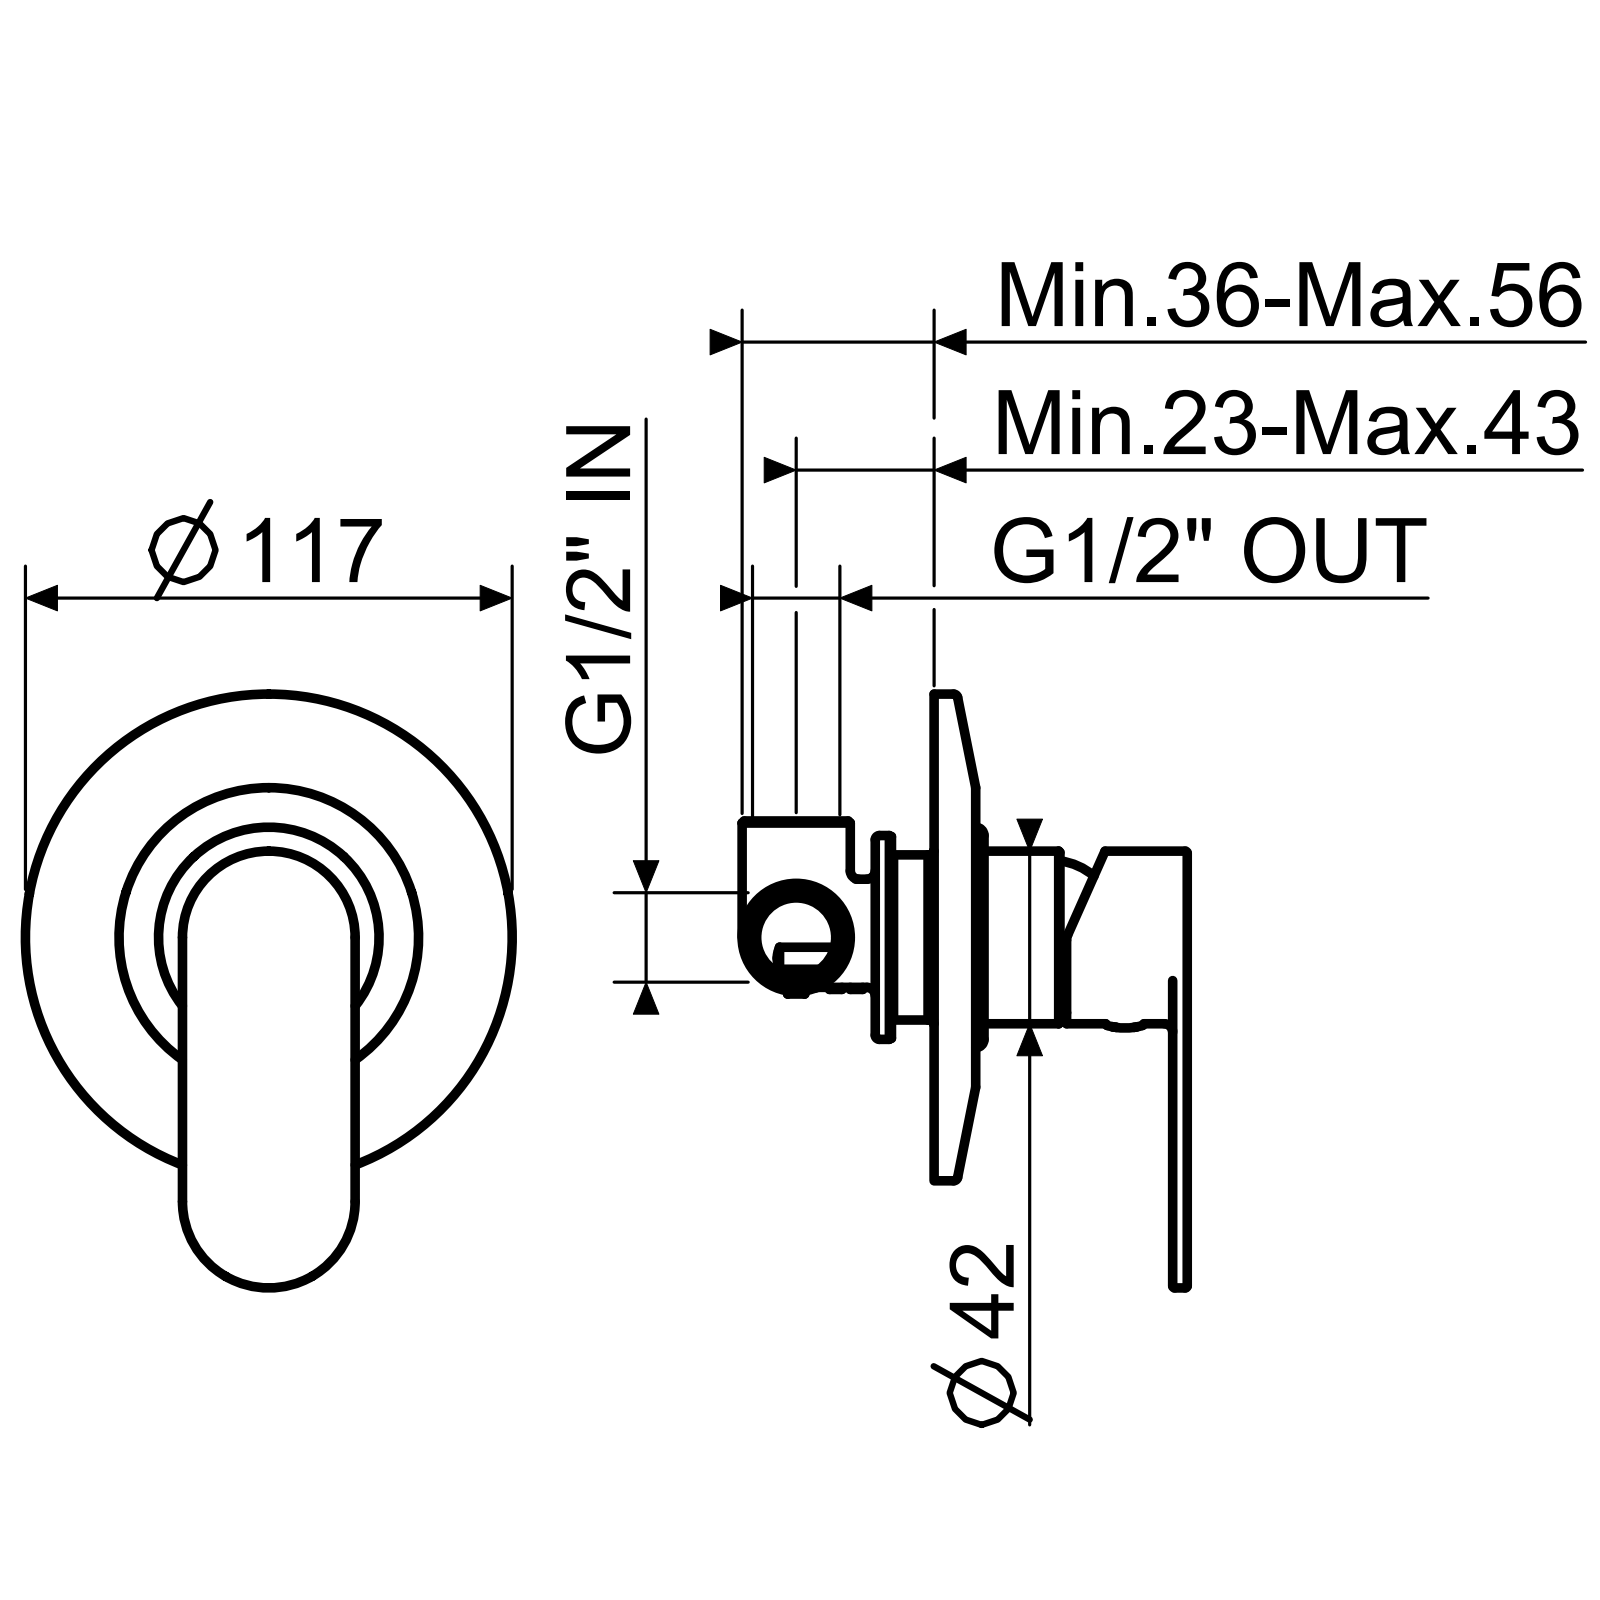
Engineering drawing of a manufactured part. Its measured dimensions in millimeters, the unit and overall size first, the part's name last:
Units: millimetres
Overall size (bounding box): 142.75 × 117 × 60.99
Round holes (diameter × count): ⌀1 ×2, ⌀8 ×2, ⌀4.2 ×1, ⌀5.1 ×1, ⌀5.5 ×1, ⌀6.5 ×1, ⌀27.7 ×1, ⌀32 ×1, ⌀37.5 ×1, ⌀40 ×1, ⌀41 ×1, ⌀45.5 ×1
Round bosses / shafts (diameter × count): ⌀117 ×1, ⌀41.5 ×1, ⌀36.8 ×1, ⌀9.2 ×1, ⌀5 ×1
Partial cylindrical surfaces — rounded edges, fillets, slot ends (radius × count): R0.5 ×27, R1 ×6, R1.6 ×6, R1.5 ×2, R3 ×2, R3.75 ×1, R3.92 ×1, R20.75 ×1
Main face-to-face distances: 50.85, 47.35, 3.5, 0.6, 47.95, 51.45, 2, 48.85, 46.85, 49.45
Volume: 35 801 mm³ · Surface area: 54 052 mm²
Bodies: 6 solids, 326 faces (88 planar, 116 cylindrical, 122 other)
Part name (STEP PRODUCT): SINMAC0010_AF1; AUNO604C001_AF1; SGUMAC0023; SCCMAC0011 (+3 more)
STEP written by: CREO PARAMETRIC BY PTC INC, 2022164 (CONFIG_CONTROL_DESIGN)
